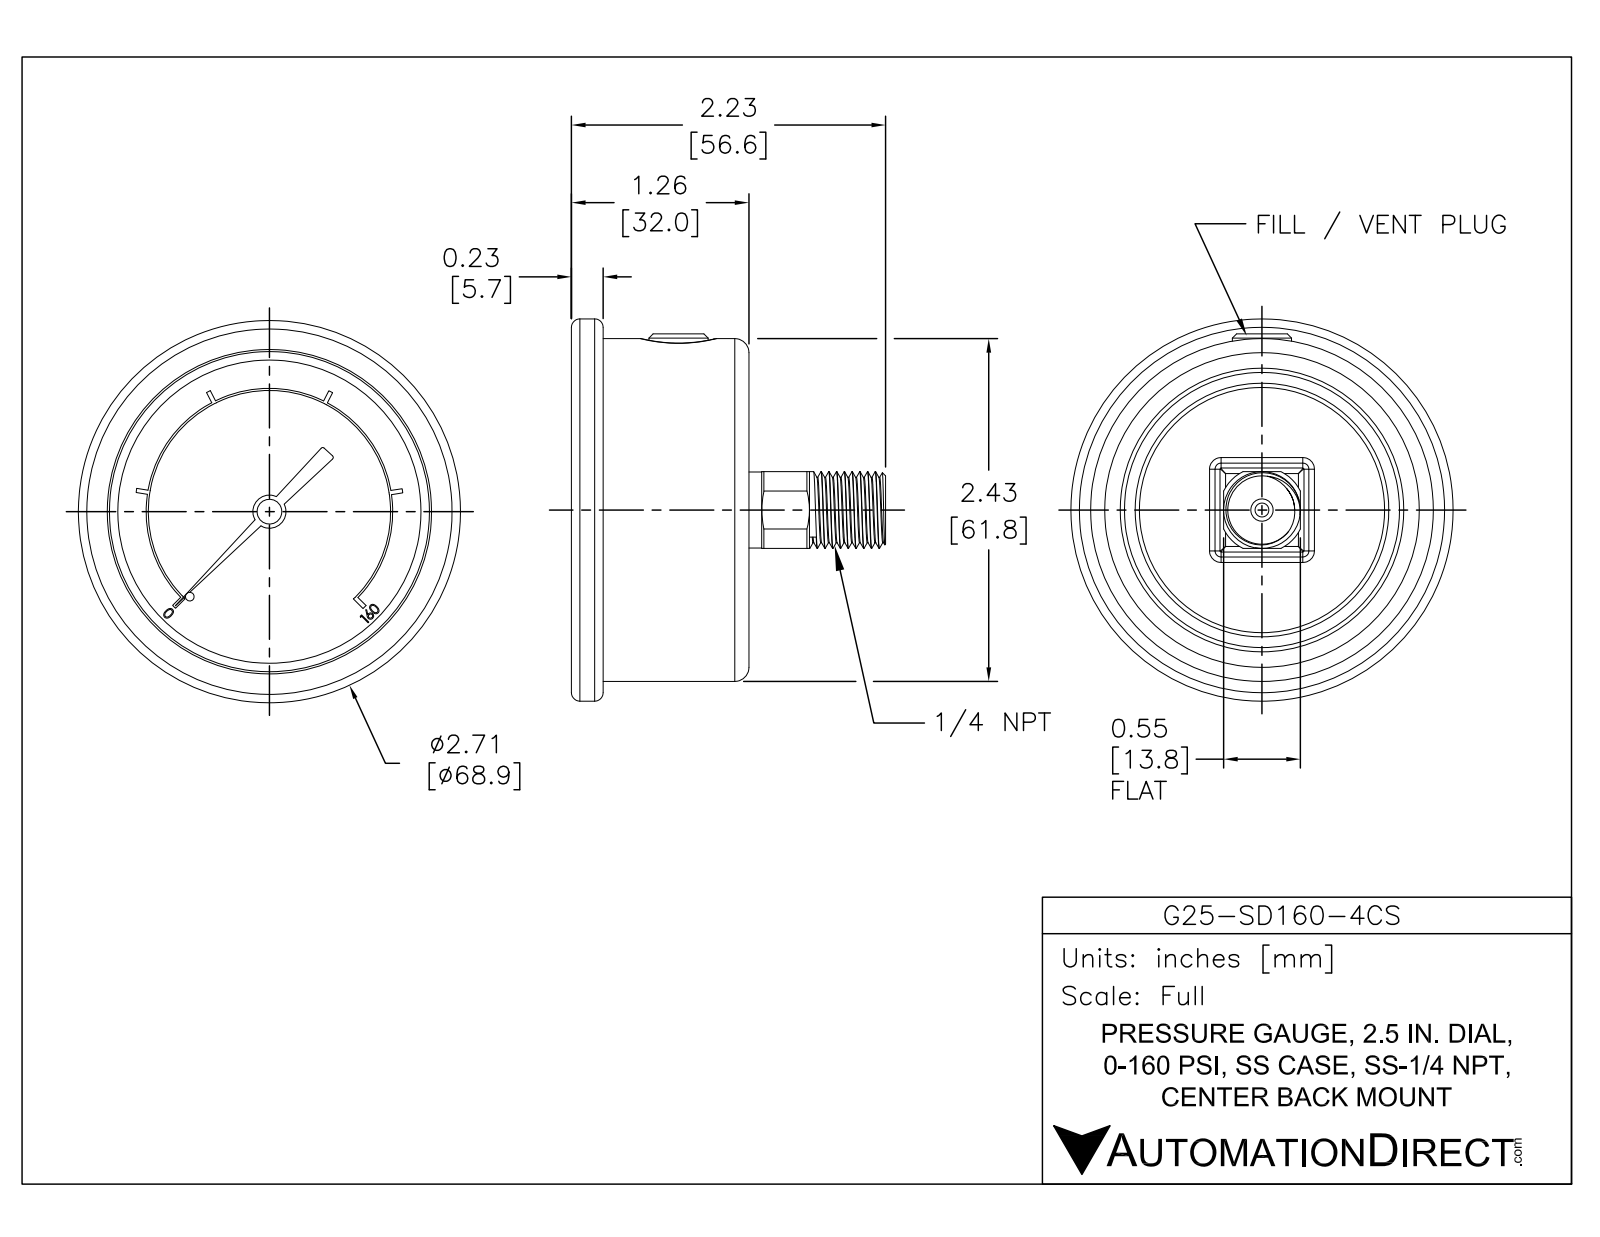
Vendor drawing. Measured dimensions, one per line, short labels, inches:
name: G25-SD160-4CS
written by: SolidWorks 2021 (AUTOMOTIVE_DESIGN)
unit: in
bodies: 1 solid, 351 faces (211 planar, 83 cylindrical, 57 other)
size: 2.713 × 2.713 × 2.23
volume: 5.168 in³; area: 24.82 in²
holes: 1× ⌀0.071, 1× ⌀0.098, 1× ⌀2.272
bosses: 1× ⌀2.713, 1× ⌀2.433, 1× ⌀0.545, 1× ⌀0.54, 1× ⌀0.42, 1× ⌀0.235, 1× ⌀0.176, 1× ⌀0.14
rounds: 8× R0.06, 2× R0.015, 1× R0.304, 1× R0.86, 1× R0.875
face distances: 0.95, 1.2, 0.25, 0.06, 1.01, 1.26, 1.035, 0.975, 0.025, 0.225
